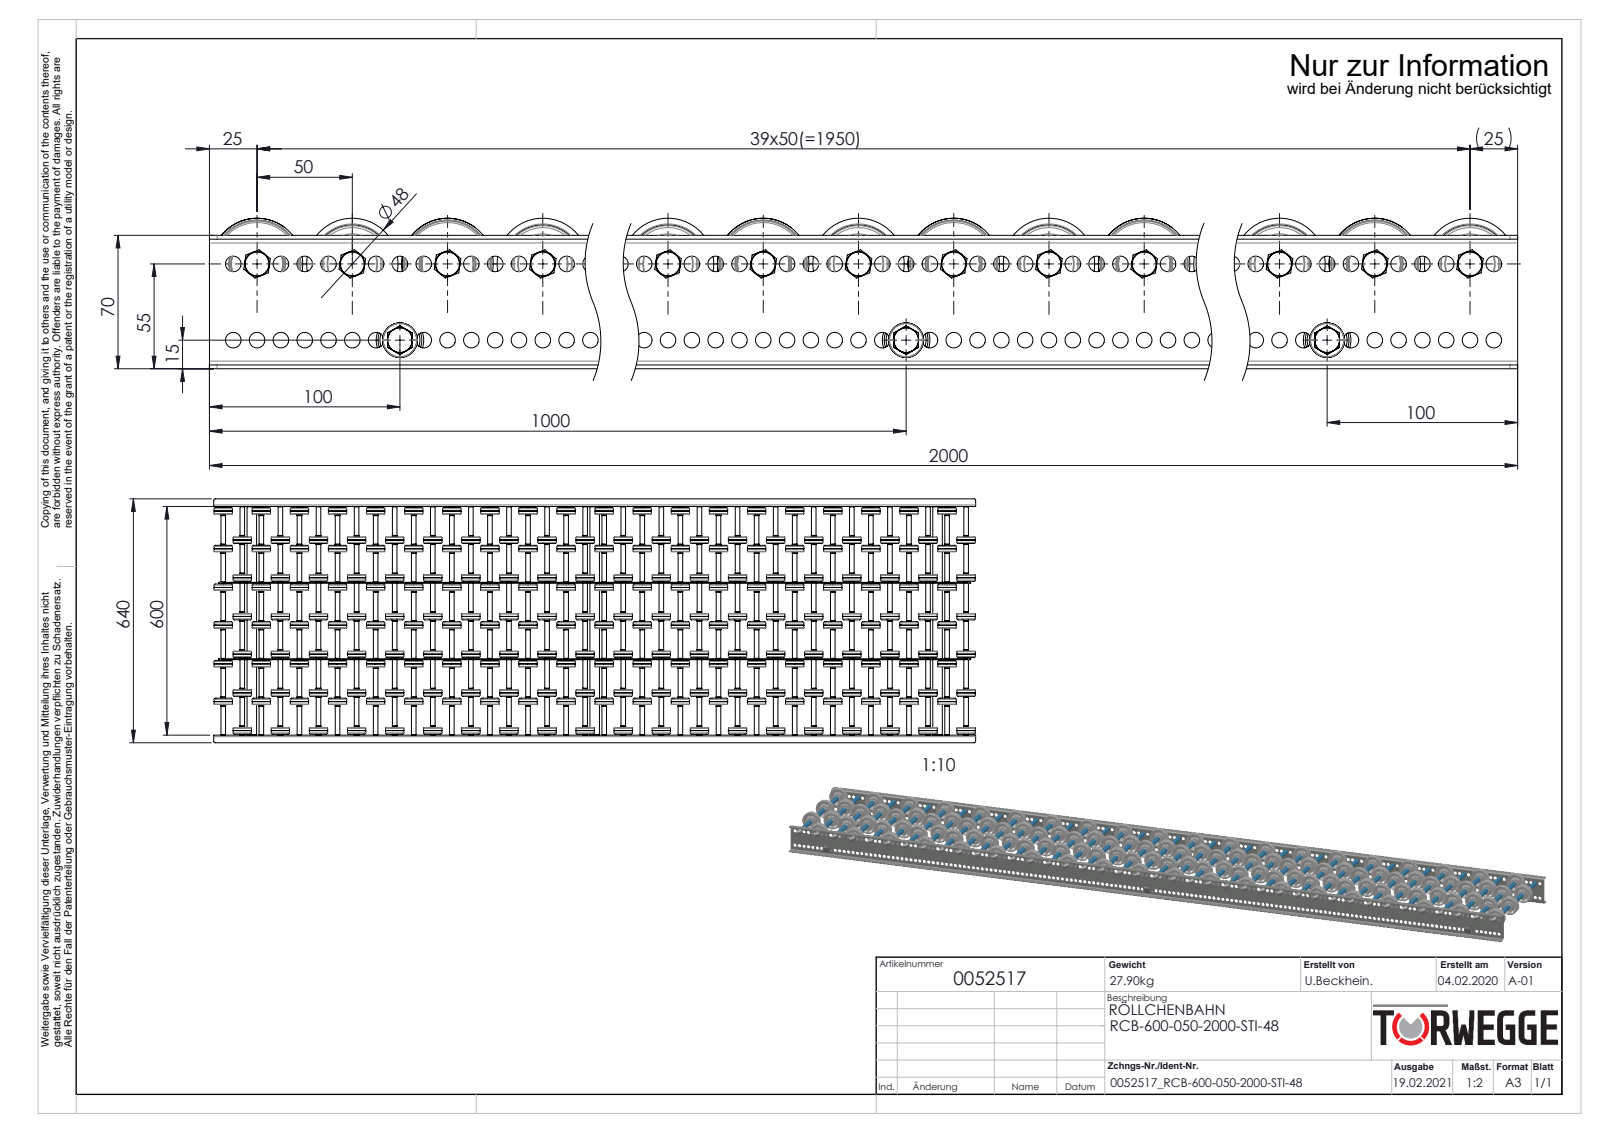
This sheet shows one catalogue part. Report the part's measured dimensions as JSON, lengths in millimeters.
{"part_name": "Röllchenachse-für-Konfiguration_EL600 Stahl; K0011528_2200-48-8; S100994_Sperrzahnschraube_M08x16-8.8-A2K; S106837_Gewindestange-M8-KFG_L620 (+6 more)", "step_written_by": "SolidWorks 2020 (AUTOMOTIVE_DESIGN)", "units": "millimeters", "bodies": {"solids": 859, "faces": 25202, "planar": 5214, "cylindrical": 9272, "other": 10716}, "overall_size": [2000, 640, 79], "volume_mm3": 8533000, "surface_area_mm2": 6319000, "round_holes": [[8.2, 318], [8.5, 79], [6.65, 40], [8, 40], [9.65, 40], [15, 40], [41, 40], [6.8, 3], [21, 3]], "round_bosses_or_shafts": [[48, 40], [13, 40], [12.5, 40], [12.4, 40], [12, 40], [11.5, 40], [25, 3], [8, 3]], "partial_cylinders_radius": [[4, 8], [2, 4], [5, 4]], "face_to_face_distances": [200.5, 76, 99, 401, 2, 88, 111, 187, 276.5, 299.5], "hole_center_spacings": [12.5, 25, 37.5, 50, 62.5, 75, 87.5, 100]}
